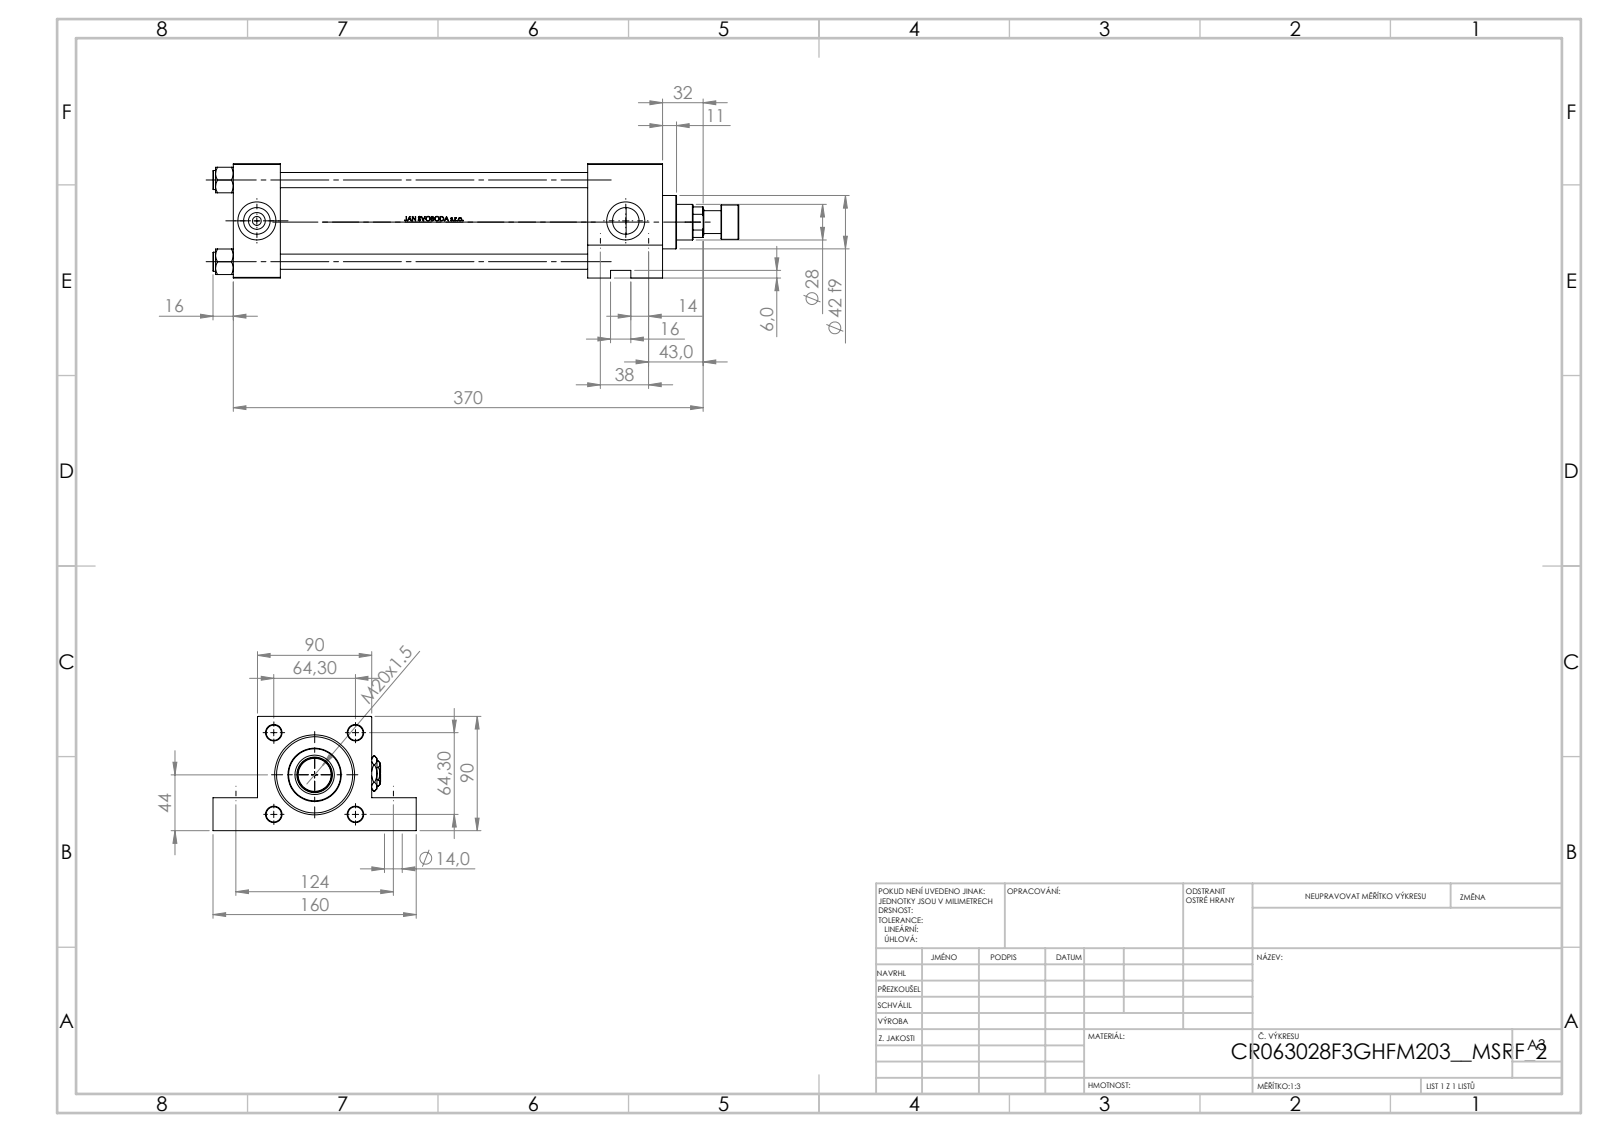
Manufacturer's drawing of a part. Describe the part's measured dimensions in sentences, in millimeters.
The part is named "Zatka_pro_OIL_PORT; V215CR_VCP_F; V215CR_F_Body; V215CR_ROD_END_F (+3 more)". Its 3-D file was written by "SolidWorks 2019 (CONFIG_CONTROL_DESIGN)". It is 14 solids with 1214 faces: 488 planar, 138 cylindrical and 588 other. Overall it measures 414 by 160 by 90 millimeters. Its volume is 1 344 000 cubic millimeters and its surface area 321 496 square millimeters. Round holes: 4 of diameter 12, 4 of diameter 14, 3 of diameter 20.96, 3 of diameter 30, 2 of diameter 7, 1 of diameter 18.5, 1 of diameter 20, 1 of diameter 28, 1 of diameter 31, 1 of diameter 50, 1 of diameter 60, 1 of diameter 63. Round bosses or shafts: 4 of diameter 15, 1 of diameter 69, 1 of diameter 42, 1 of diameter 27, 1 of diameter 18. The main face-to-face distances are 90, 37, 301, 338, 279, 242, 59, 26, 64, 35. The hole center spacings are 64.3, 38, 44.77, 46.18, 90.93, 124, 129.69, 10.
